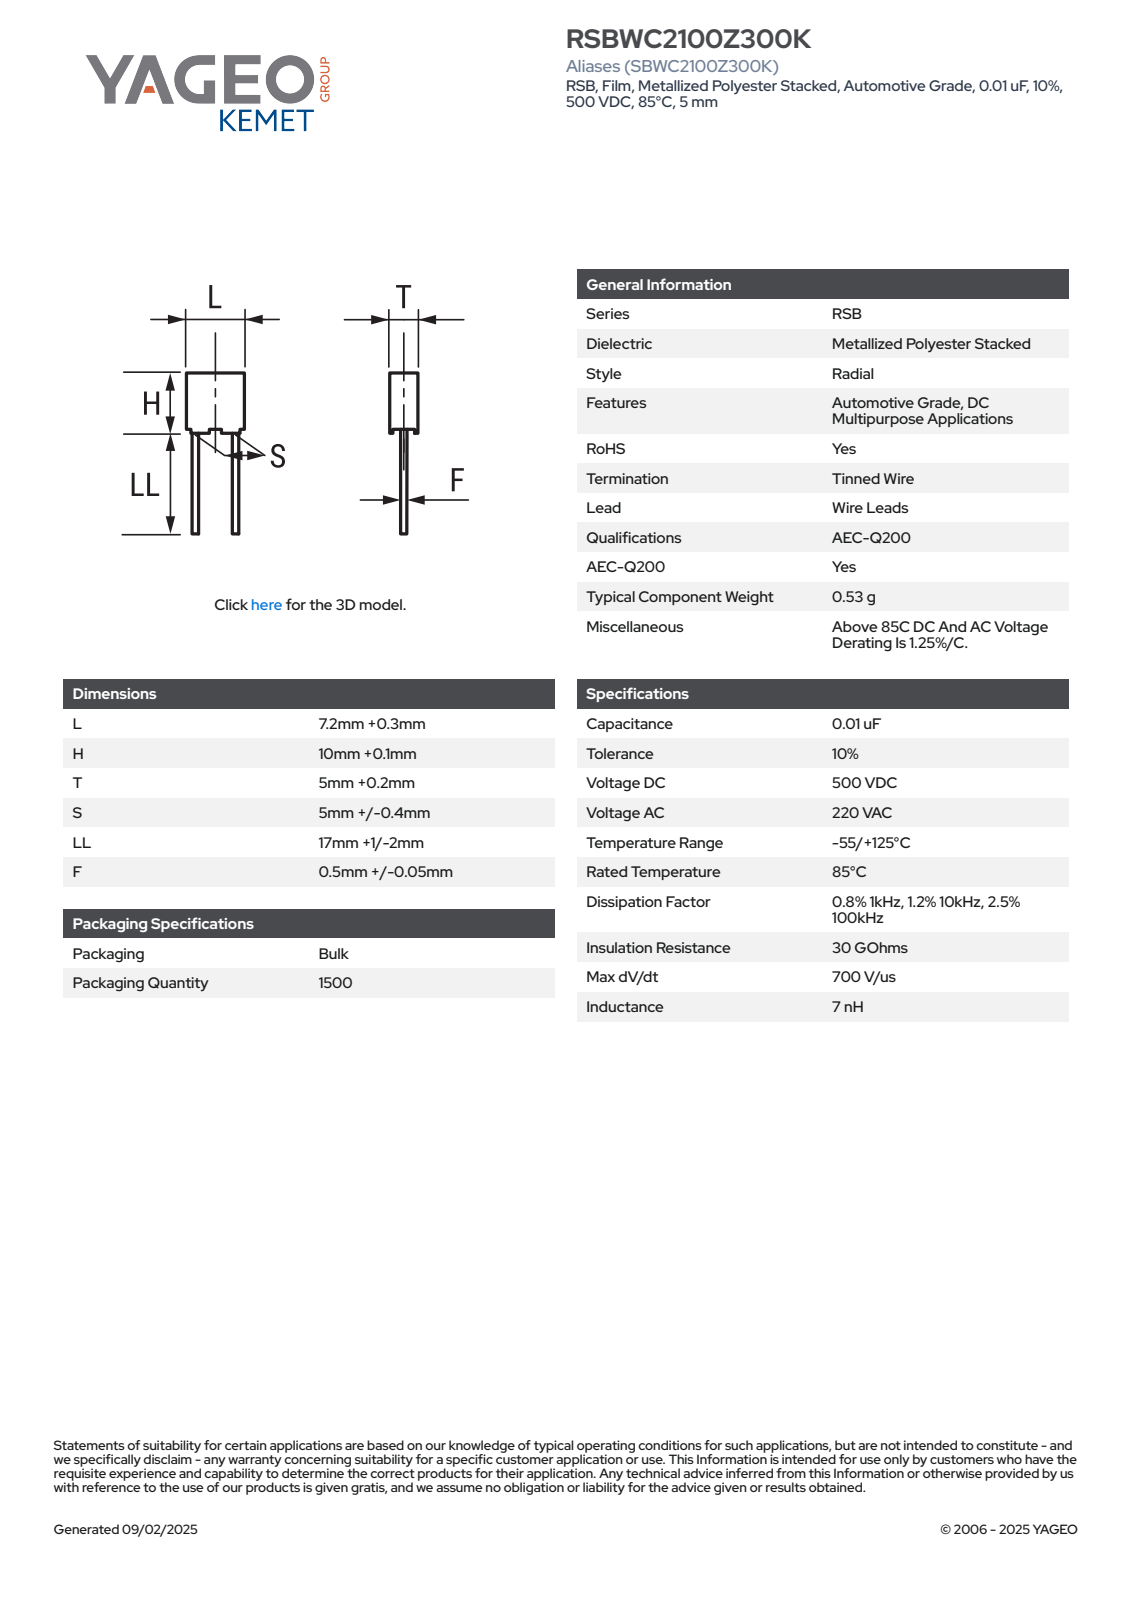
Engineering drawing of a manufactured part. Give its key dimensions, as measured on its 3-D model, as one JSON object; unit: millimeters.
{"part_name": "CFR_RB3_7.2X10X5_L7.5H10.1T5.2S5LL18F0.65", "step_written_by": "SolidWorks 2014 (AUTOMOTIVE_DESIGN)", "units": "millimeters", "bodies": {"solids": 4, "faces": 85, "planar": 77, "cylindrical": 8, "other": 0}, "overall_size": [28.1, 7.5, 5.21], "volume_mm3": 380, "surface_area_mm2": 425, "round_bosses_or_shafts": [[0.65, 2]], "partial_cylinders_radius": [[0.5, 4]], "face_to_face_distances": [5.2, 7.5, 9.35, 4.95, 7.25, 0.75, 10.1, 4.7, 7, 0.35]}
